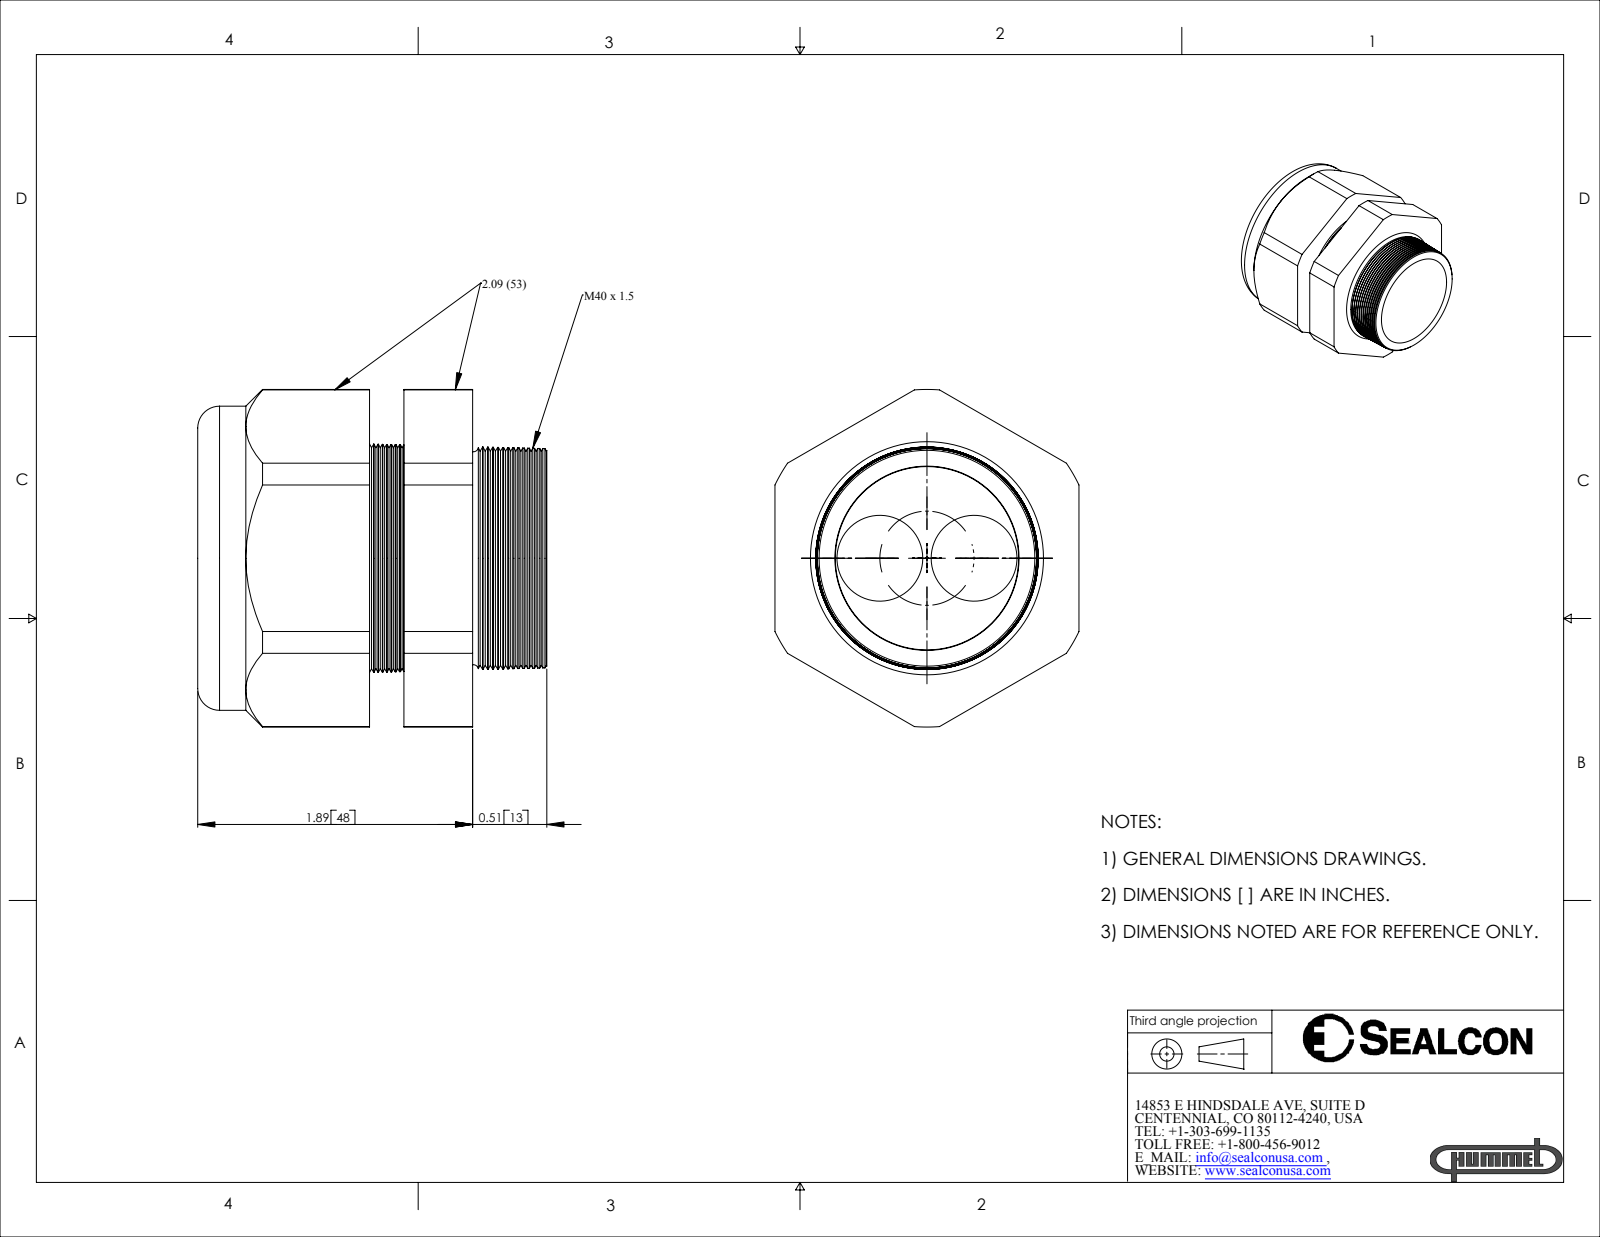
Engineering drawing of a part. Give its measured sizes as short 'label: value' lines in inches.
name: CD40M4-BK
written by: SolidWorks 2007 (CONFIG_CONTROL_DESIGN)
unit: in
bodies: 2 solids, 193 faces (21 planar, 24 cylindrical, 148 other)
size: 2.4 × 2.32 × 2.09
volume: 4.734 in³; area: 40.85 in²
holes: 2× ⌀0.59, 1× ⌀1.24, 1× ⌀1.26
bosses: 1× ⌀2.09
rounds: 1× R1.16
face distances: 2.09, 0.237, 0.709, 0.472, 1.181, 1.418, 1.89, 0.5, 0.681, 0.918
hole spacings: 0.324, 0.648
